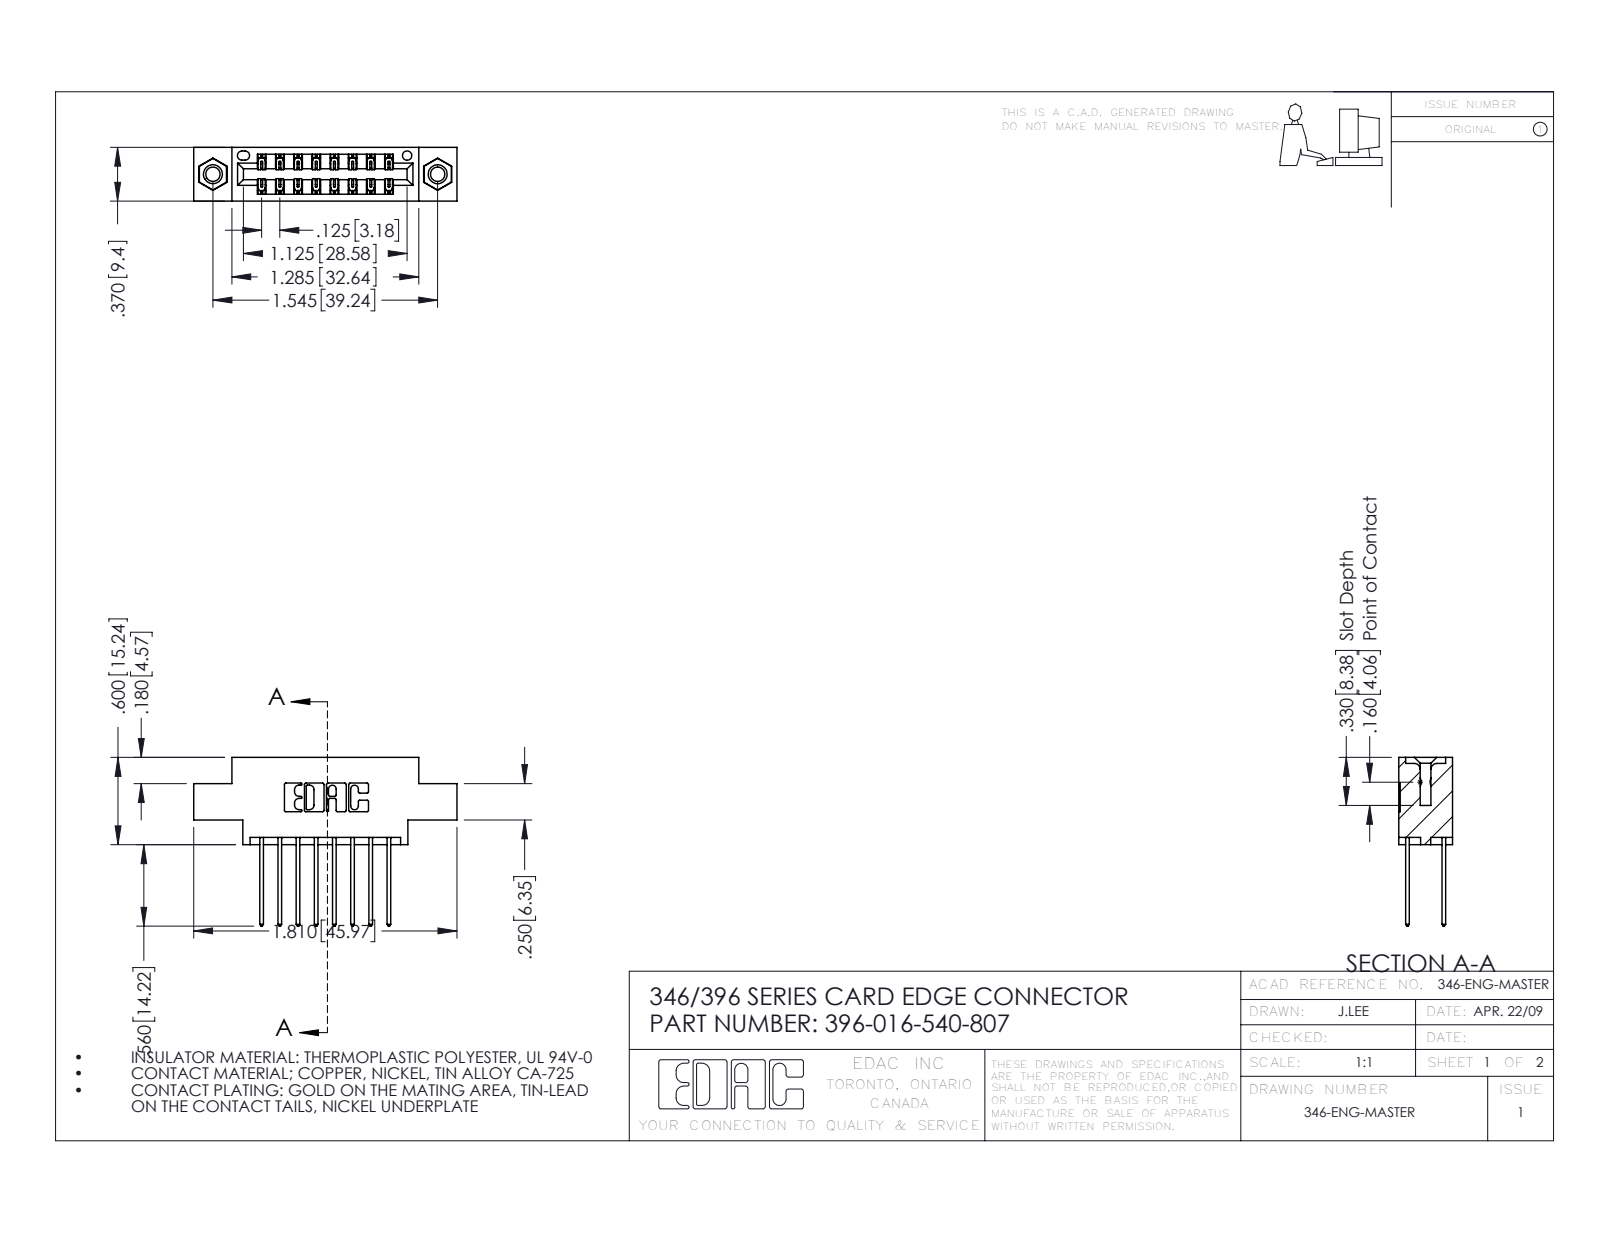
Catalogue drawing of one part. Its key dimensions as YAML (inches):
part_name: "396-016-540-807; 345-292-001_345-293-140; 345-250-001_345-250-005-103; 346 Part_0.170 Offset - 0.156 Dia-TI"
step_written_by: "SolidWorks 2016 (CONFIG_CONTROL_DESIGN)"
units: inches
bodies: {solids: 19, faces: 1018, planar: 672, cylindrical: 330, other: 16}
overall_size: [1.81, 1.16, 0.37]
volume: 0.251
surface_area: 8.707
round_holes:
  - {diameter: 0.098, count: 2}
  - {diameter: 0.125, count: 2}
  - {diameter: 0.156, count: 2}
  - {diameter: 0.064, count: 1}
round_bosses_or_shafts:
  - {diameter: 0.155, count: 2}
partial_cylinders:
  - {radius: 0.006, count: 24}
  - {radius: 0.01, count: 22}
  - {radius: 0.01, count: 16}
  - {radius: 0.007, count: 6}
  - {radius: 0.031, count: 6}
  - {radius: 0.026, count: 3}
  - {radius: 0.014, count: 2}
  - {radius: 0.022, count: 2}
face_to_face_distances: [0.25, 0.048, 0.322, 0.37, 0.072, 0.298, 0.025, 0.275, 0.222, 0.148]
hole_center_spacings: [0.246, 1.341, 1.545]
